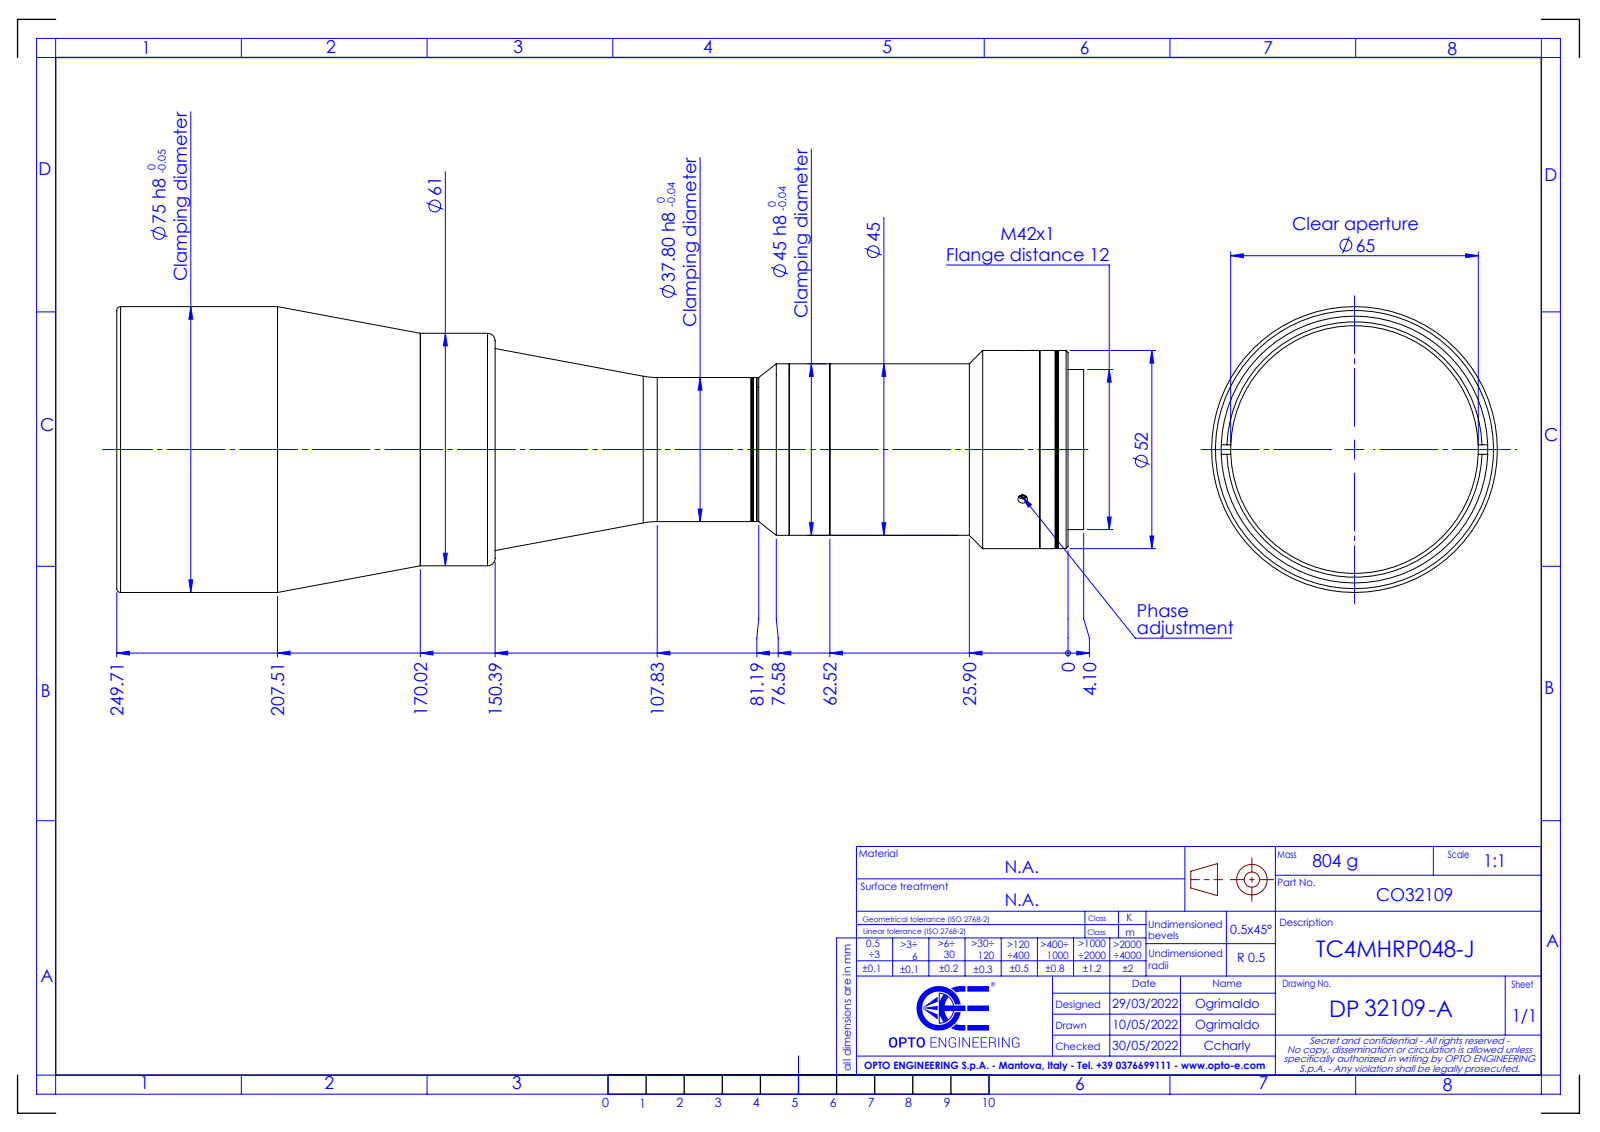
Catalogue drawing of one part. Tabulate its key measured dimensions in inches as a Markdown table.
| quantity | value |
| --- | --- |
| part name | DP32109-A_TC4MHRP048-J |
| STEP written by | SolidWorks 2021 (CONFIG_CONTROL_DESIGN) |
| units | inches |
| bodies | 0 solids, 100 faces (24 planar, 52 cylindrical, 24 other) |
| overall size | 9.993 × 2.953 × 2.953 |
| round holes (diameter × count) | 0.098 × 3, 1.496 × 1, 1.614 × 1, 2.087 × 1, 2.559 × 1, 2.756 × 1 |
| round bosses / shafts (diameter × count) | 2.953 × 1, 2.402 × 1, 2.047 × 1, 2.039 × 1, 1.772 × 1, 1.654 × 1, 1.488 × 1 |
| main face-to-face distances | 0.191, 0.157, 0.033, 0.291, 0.134, 0.101, 6.402, 6.56, 6.593, 6.694 |
